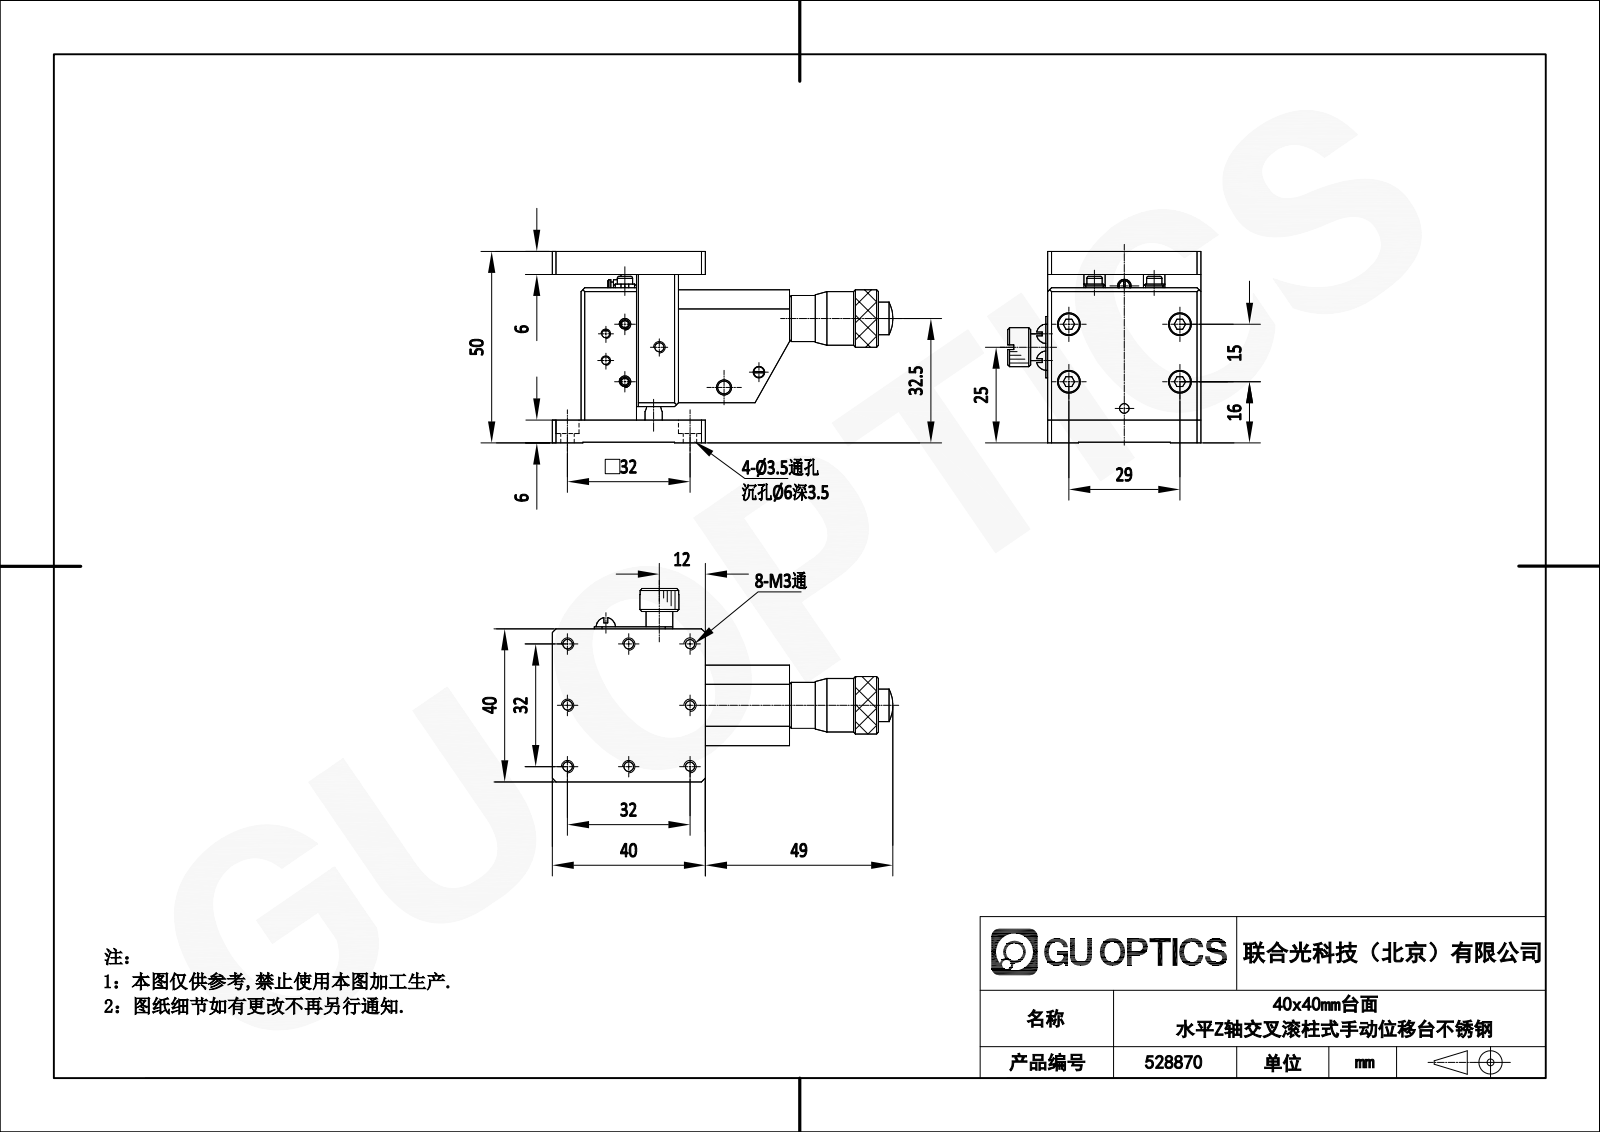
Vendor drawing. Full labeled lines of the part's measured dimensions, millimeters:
Part name (STEP PRODUCT): 528870
STEP written by: SolidWorks 2020 (CONFIG_CONTROL_DESIGN)
Units: millimetres
Bodies: 0 solids, 347 faces (186 planar, 125 cylindrical, 36 other)
Overall size (bounding box): 88.75 × 52.5 × 50
Round holes (diameter × count): ⌀6 ×18, ⌀3.5 ×16, ⌀2.46 ×13, ⌀2.01 ×8, ⌀2.4 ×8, ⌀4.3 ×8, ⌀2.46 ×6, ⌀2.6 ×2, ⌀3.2 ×2, ⌀4 ×2, ⌀2 ×1, ⌀3 ×1
Round bosses / shafts (diameter × count): ⌀5 ×4, ⌀6 ×2, ⌀15 ×1, ⌀14 ×1, ⌀12 ×1, ⌀10 ×1, ⌀8.5 ×1, ⌀6.35 ×1
Partial cylindrical surfaces — rounded edges, fillets, slot ends (radius × count): R0.5 ×4, R2 ×4, R1 ×2, R1.7 ×2, R4 ×2, R3.5 ×1, R4.75 ×1
Main face-to-face distances: 9.5, 6, 40, 30.5, 0.5, 6.5, 44, 3.5, 7, 38
Hole centre spacings: 16, 25.3, 8, 11.31, 35.78, 17.89, 32, 24
